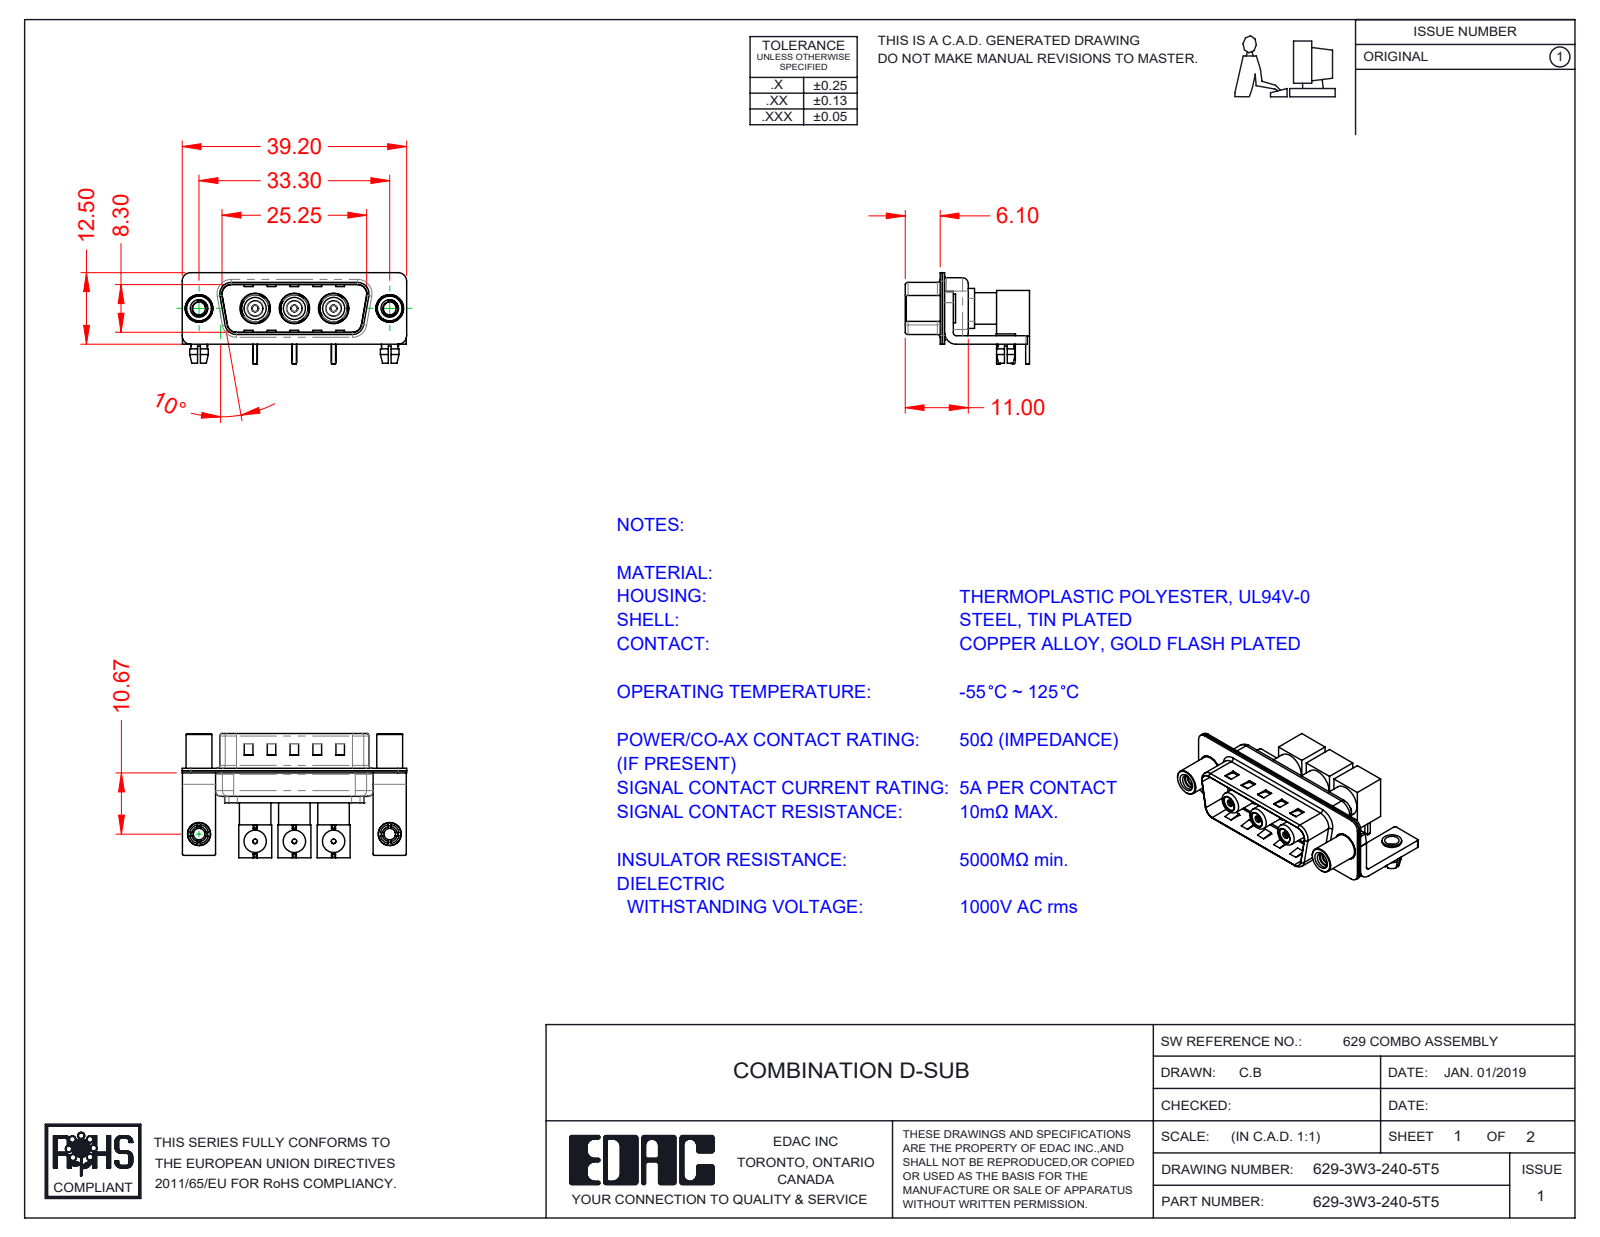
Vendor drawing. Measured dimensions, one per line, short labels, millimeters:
name: 629Combo Housing_3W3; Co-Ax Jack Assy_RA; 629Combo Board Lock; 629Combo Shell Rear_15 Contacts (+8 more)
written by: SolidWorks 2020 (CONFIG_CONTROL_DESIGN)
unit: mm
bodies: 30 solids, 976 faces (380 planar, 426 cylindrical, 170 other)
size: 39.2 × 21.71 × 16
volume: 3 130 mm³; area: 8 648 mm²
holes: 5× ⌀2.5, 3× ⌀0.8, 3× ⌀1.1, 3× ⌀1.2, 3× ⌀1.5, 3× ⌀1.6, 3× ⌀2.7, 3× ⌀3.1, 3× ⌀3.4, 3× ⌀3.9, 3× ⌀4.1, 3× ⌀4.85
bosses: 6× ⌀0.8, 5× ⌀4, 5× ⌀3.3, 5× ⌀2.9, 3× ⌀5.5, 3× ⌀5.2, 3× ⌀4.8, 3× ⌀4.73
rounds: 16× R0.25, 16× R1.5, 13× R2, 9× R0.5, 8× R1.6, 4× R0.6, 4× R0.65, 4× R0.9
face distances: 0.4, 0.8, 1.5, 5.75, 9.5, 1.4, 8.7, 9.1, 1.1, 0.35
hole spacings: 6.85, 13.7, 9.88, 16.7, 23.53, 9.8, 16.65, 23.5
